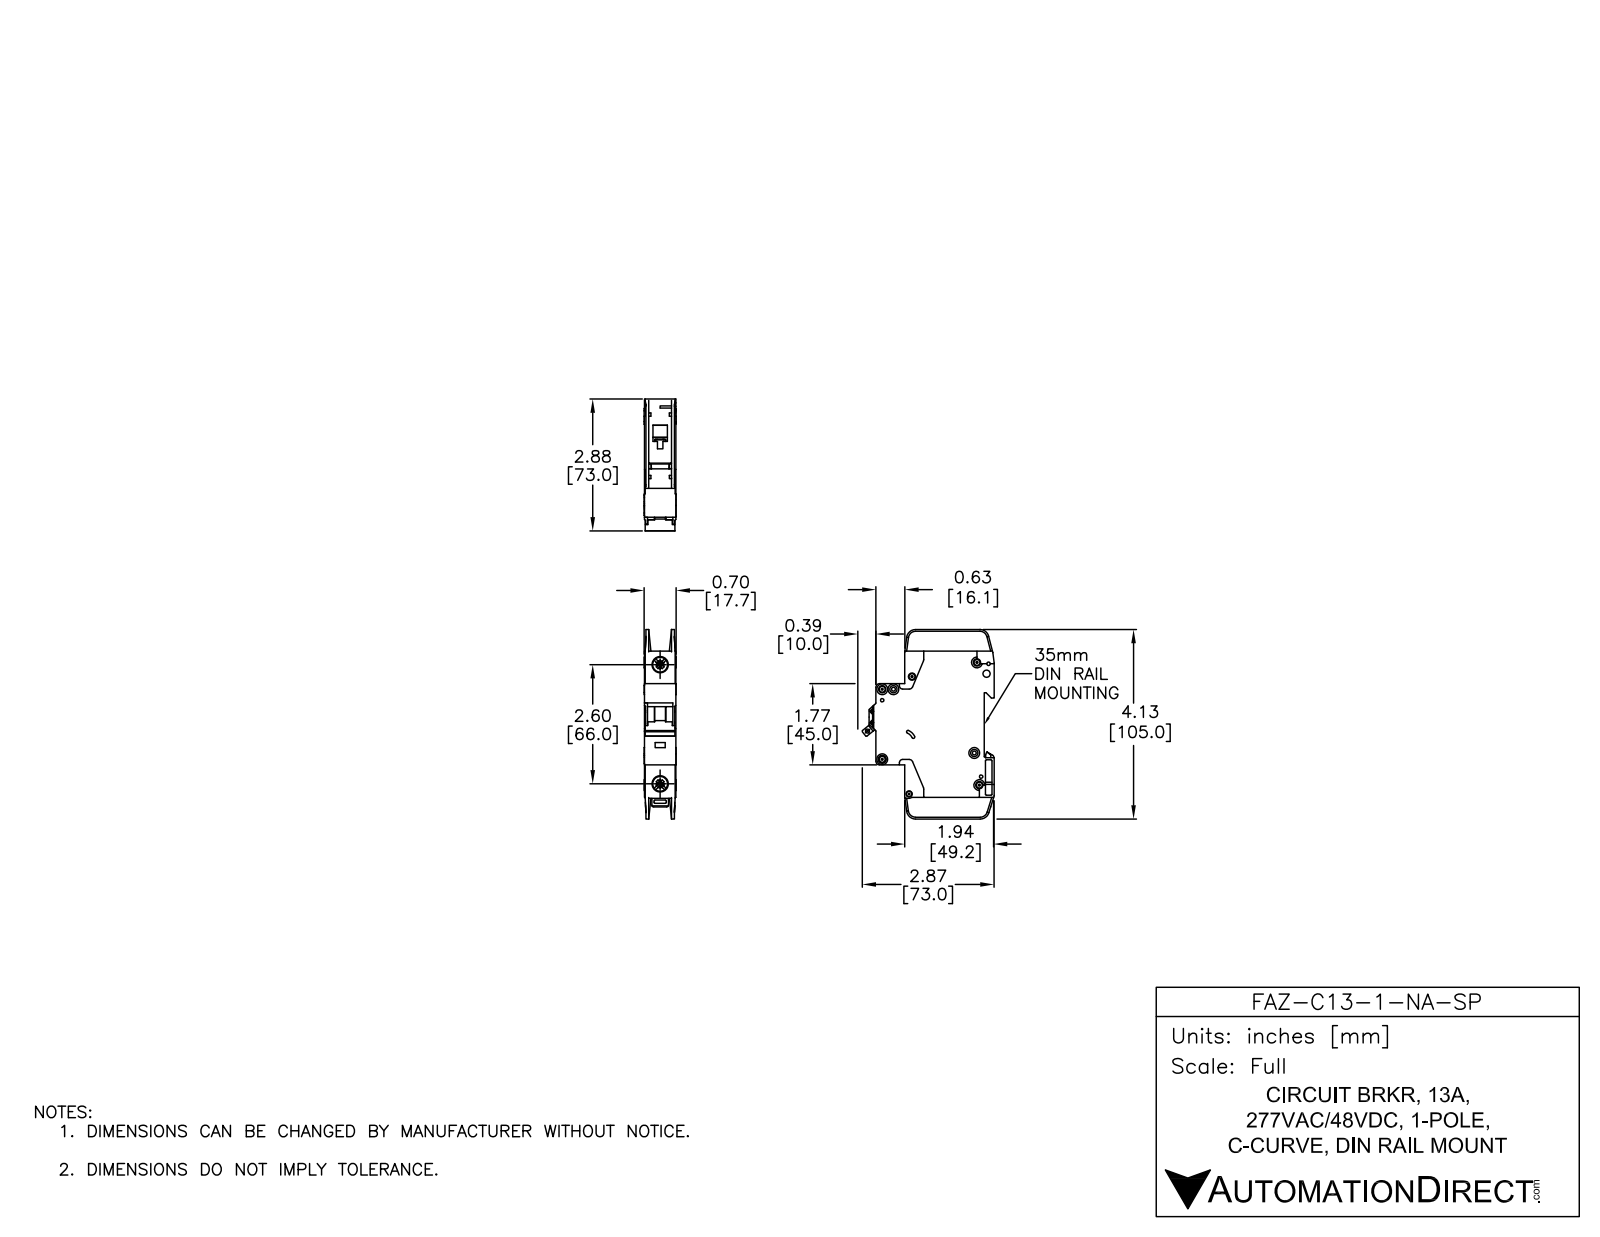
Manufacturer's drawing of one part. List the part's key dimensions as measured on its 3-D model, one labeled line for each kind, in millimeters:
Part name (STEP PRODUCT): FAZ-C13-1-NA-SP
STEP written by: SolidWorks 2014 (AUTOMOTIVE_DESIGN)
Units: millimetres
Bodies: 3 solids, 784 faces (409 planar, 263 cylindrical, 112 other)
Overall size (bounding box): 105 × 73.04 × 17.7
Volume: 77 695 mm³ · Surface area: 24 740 mm²
Round holes (diameter × count): ⌀3.6 ×7, ⌀1.09 ×2, ⌀1.5 ×2, ⌀4 ×2, ⌀7.15 ×2, ⌀8.2 ×2, ⌀1.9 ×1, ⌀2.15 ×1, ⌀2.2 ×1, ⌀2.55 ×1, ⌀3.3 ×1, ⌀3.4 ×1
Round bosses / shafts (diameter × count): ⌀6 ×7, ⌀2.5 ×1
Partial cylindrical surfaces — rounded edges, fillets, slot ends (radius × count): R0.25 ×29, R0.5 ×18, R1 ×10, R2 ×10, R5 ×5, R4 ×4, R1.8 ×3, R0.2 ×2
Main face-to-face distances: 17.5, 15.05, 0.7, 2.45, 1.75, 15.75, 13.3, 14, 12.6, 2
Hole centre spacings: 6.2, 5.19, 6.1, 8.19, 8.56, 8.7, 11.11, 12.45
